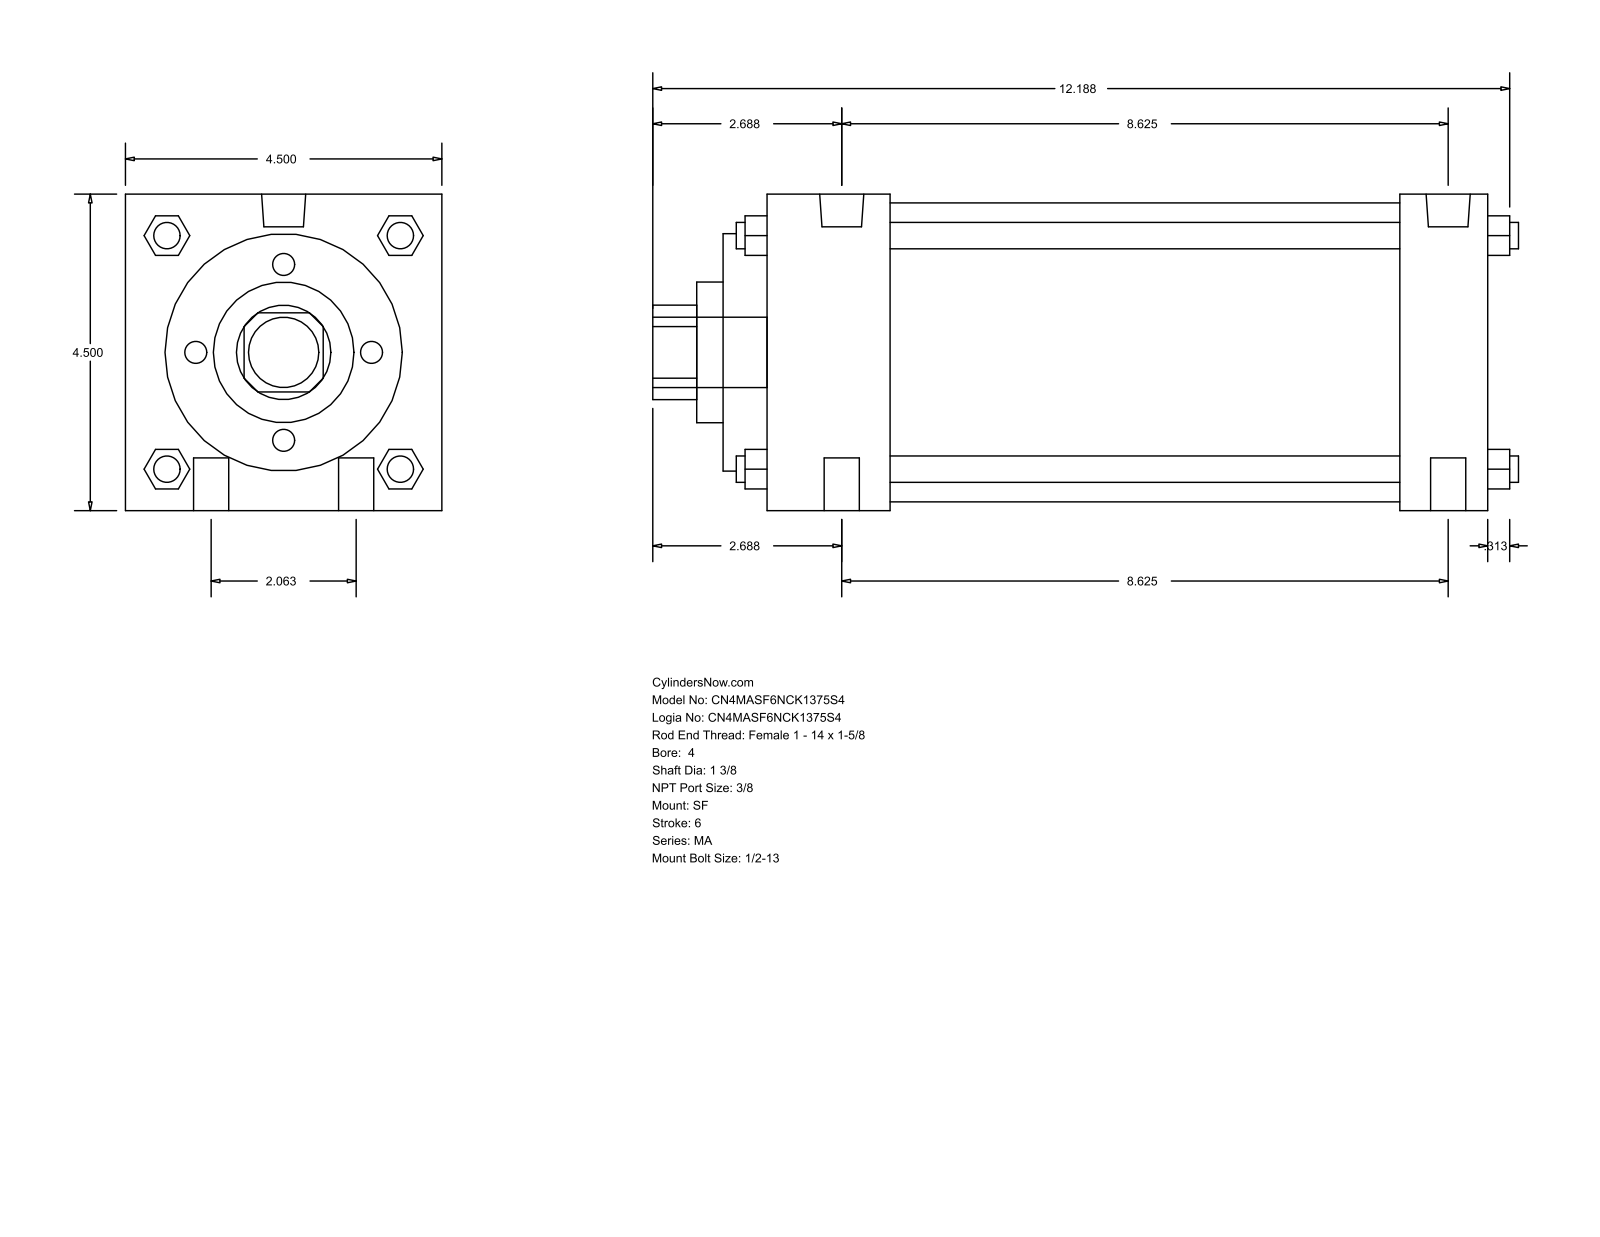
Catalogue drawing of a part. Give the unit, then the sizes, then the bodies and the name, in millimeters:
Units: millimetres
Overall size (bounding box): 312.74 × 114.3 × 114.3
Round holes (diameter × count): ⌀34.92 ×1, ⌀50.8 ×1, ⌀85.72 ×1, ⌀107.95 ×1
Round bosses / shafts (diameter × count): ⌀12.7 ×4, ⌀9.53 ×4, ⌀15.93 ×2, ⌀11.11 ×2, ⌀25.4 ×1
Partial cylindrical surfaces — rounded edges, fillets, slot ends (radius × count): R17.06 ×1
Main face-to-face distances: 114.3, 260.35, 276.22, 15.87, 244.48, 228.61, 31.74, 60.32, 44.45, 184.16
Bodies: 0 solids, 126 faces (95 planar, 31 cylindrical, 0 other)
Part name (STEP PRODUCT): MA_SF__0400_1.375
STEP written by: GSSL Pune (CONFIG_CONTROL_DESIGN)
